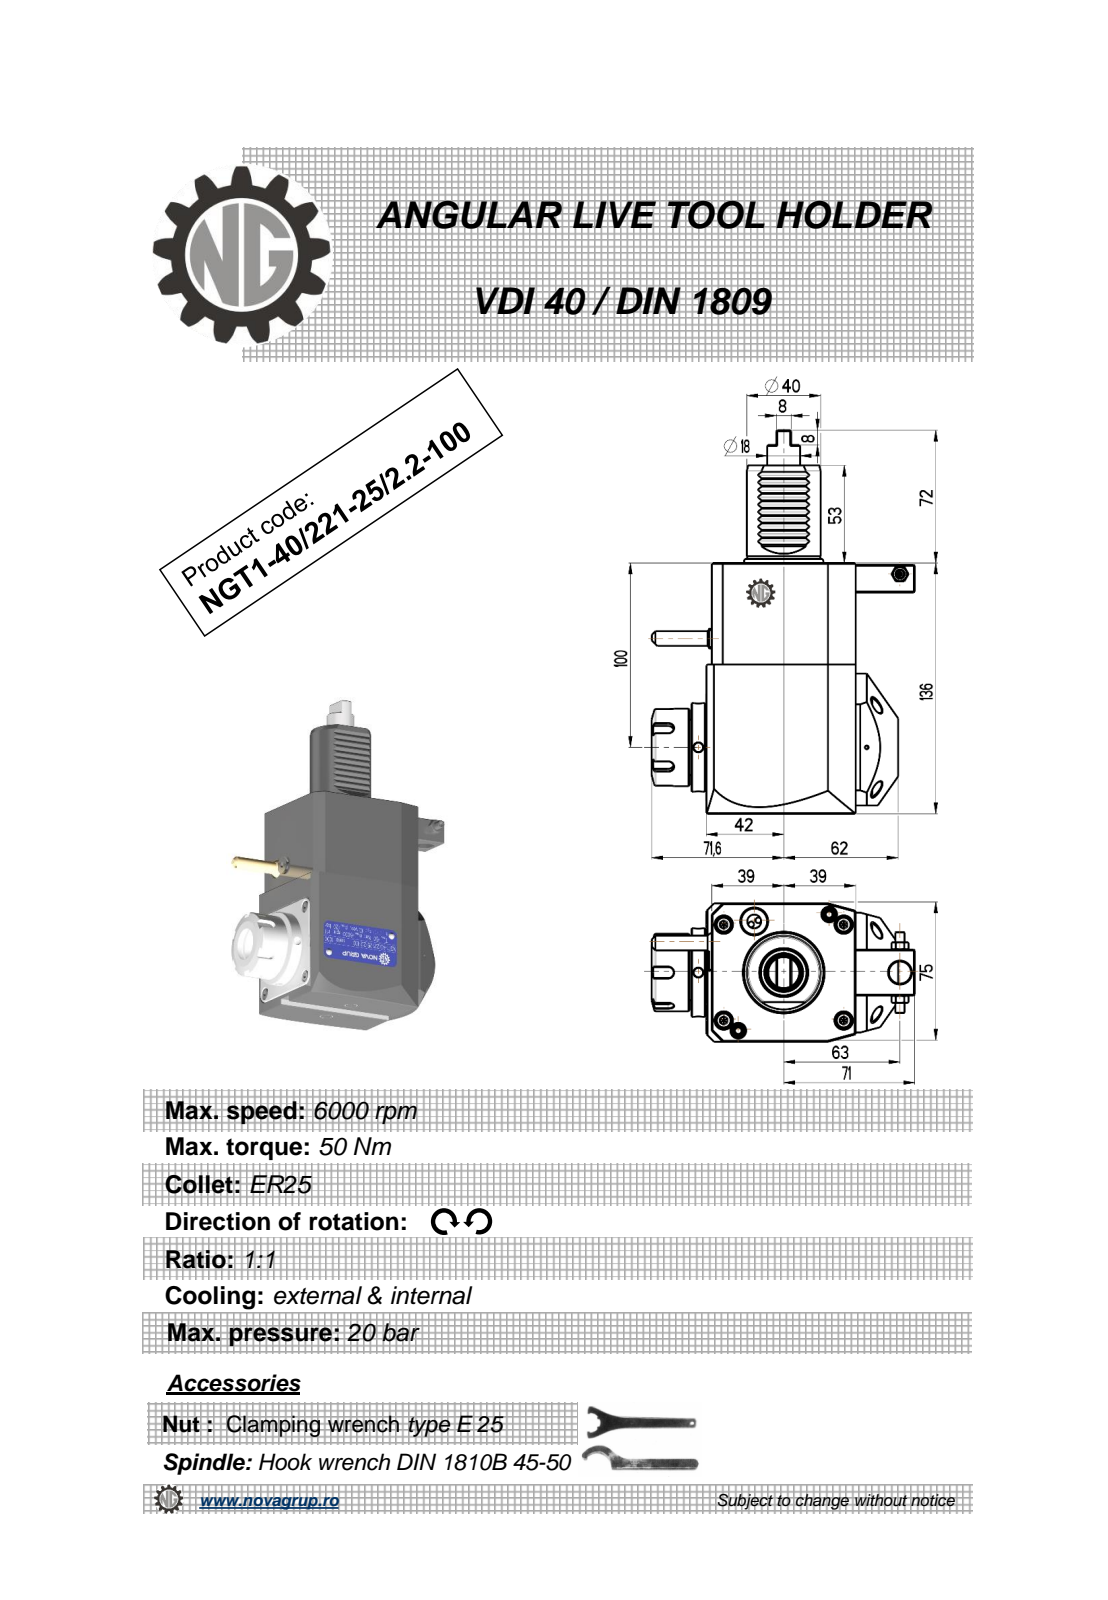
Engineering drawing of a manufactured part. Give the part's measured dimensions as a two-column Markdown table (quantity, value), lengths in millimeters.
| quantity | value |
| --- | --- |
| part name | NGT1_40_221_25_2_2_100 |
| STEP written by | PRO/ENGINEER BY PARAMETRIC TECHNOLOGY CORPORATION, 2010280 (CONFIG_CONTROL_DESIGN) |
| units | millimeters |
| bodies | 1 solid, 428 faces (190 planar, 89 cylindrical, 149 other) |
| overall size | 208 × 142.6 × 76.6 |
| volume | 981 750 mm³ |
| surface area | 75 621 mm² |
| round holes (diameter × count) | 5 × 3, 3 × 1, 4.2 × 1, 9.5 × 1, 12 × 1, 20.3 × 1 |
| round bosses / shafts (diameter × count) | 48 × 1, 42 × 1, 40 × 1, 37.5 × 1, 33 × 1, 17.8 × 1, 11.2 × 1, 8.96 × 1 |
| partial cylindrical surfaces (radius × count) | 0.26 × 12, 0.3 × 10, 0.22 × 6, 3 × 5, 0.8 × 2, 0.5 × 1, 40 × 1 |
| main face-to-face distances | 75, 136, 78, 81, 3, 2.8, 80.8, 8, 11, 7.5 |
| hole center spacings | 37.12, 61.13, 92.5, 109.25, 144.12 |
